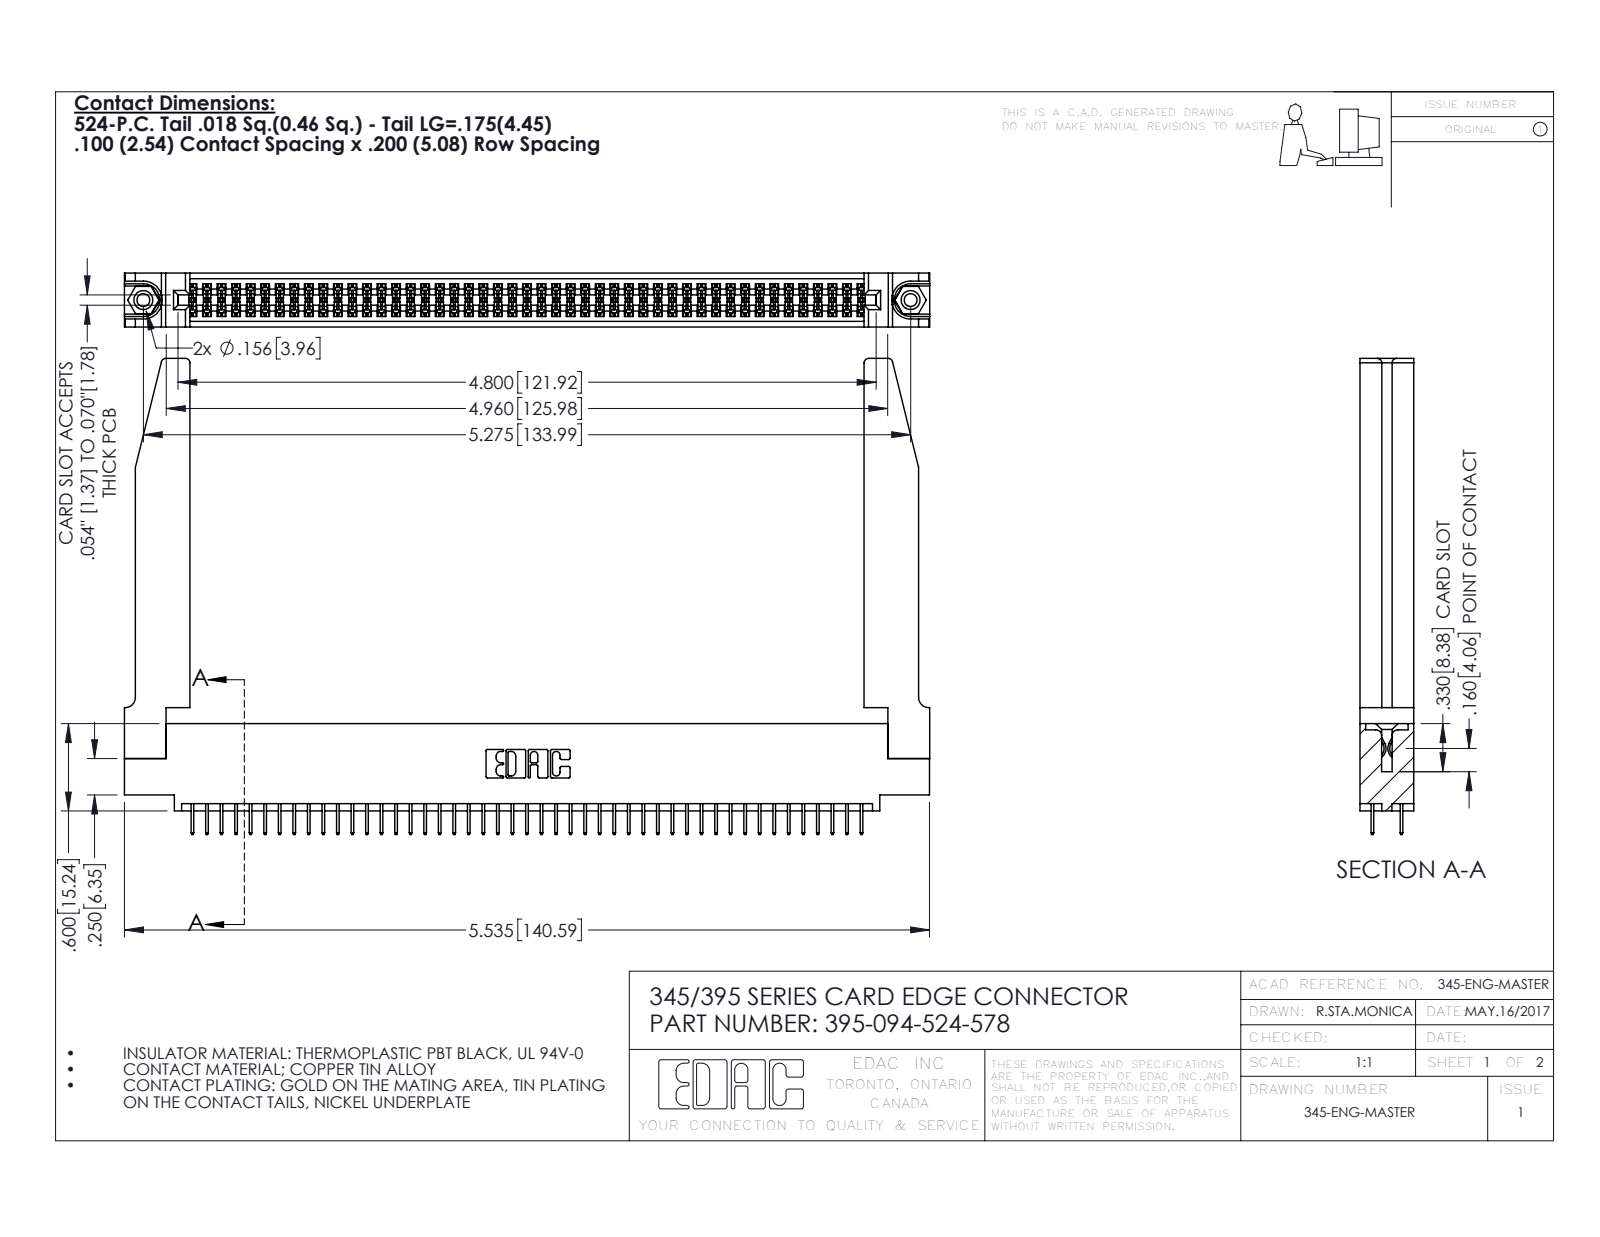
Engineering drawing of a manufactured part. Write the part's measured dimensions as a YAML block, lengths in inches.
part_name: "345-220-078_345-220-078; 345-250-001_345-250-001-102; 395-094-524-578; 345 Part_0.110 Offset - 0.156 Dia-TH (+1 more)"
step_written_by: "SolidWorks 2016 (CONFIG_CONTROL_DESIGN)"
units: inches
bodies: {solids: 99, faces: 5440, planar: 3892, cylindrical: 1496, other: 52}
overall_size: [5.536, 3.272, 0.37]
volume: 1.297
surface_area: 41.22
round_holes:
  - {diameter: 0.089, count: 2}
  - {diameter: 0.125, count: 2}
  - {diameter: 0.156, count: 2}
  - {diameter: 0.064, count: 1}
round_bosses_or_shafts:
  - {diameter: 0.155, count: 2}
partial_cylinders:
  - {radius: 0.006, count: 141}
  - {radius: 0.01, count: 22}
  - {radius: 0.03, count: 8}
  - {radius: 0.007, count: 6}
  - {radius: 0.031, count: 6}
  - {radius: 0.026, count: 3}
  - {radius: 0.014, count: 2}
  - {radius: 0.019, count: 2}
face_to_face_distances: [0.37, 0.072, 0.298, 0.2, 0.098, 0.272, 0.025, 0.225, 0.072, 0.148]
hole_center_spacings: [0.27, 5.039, 5.275]
